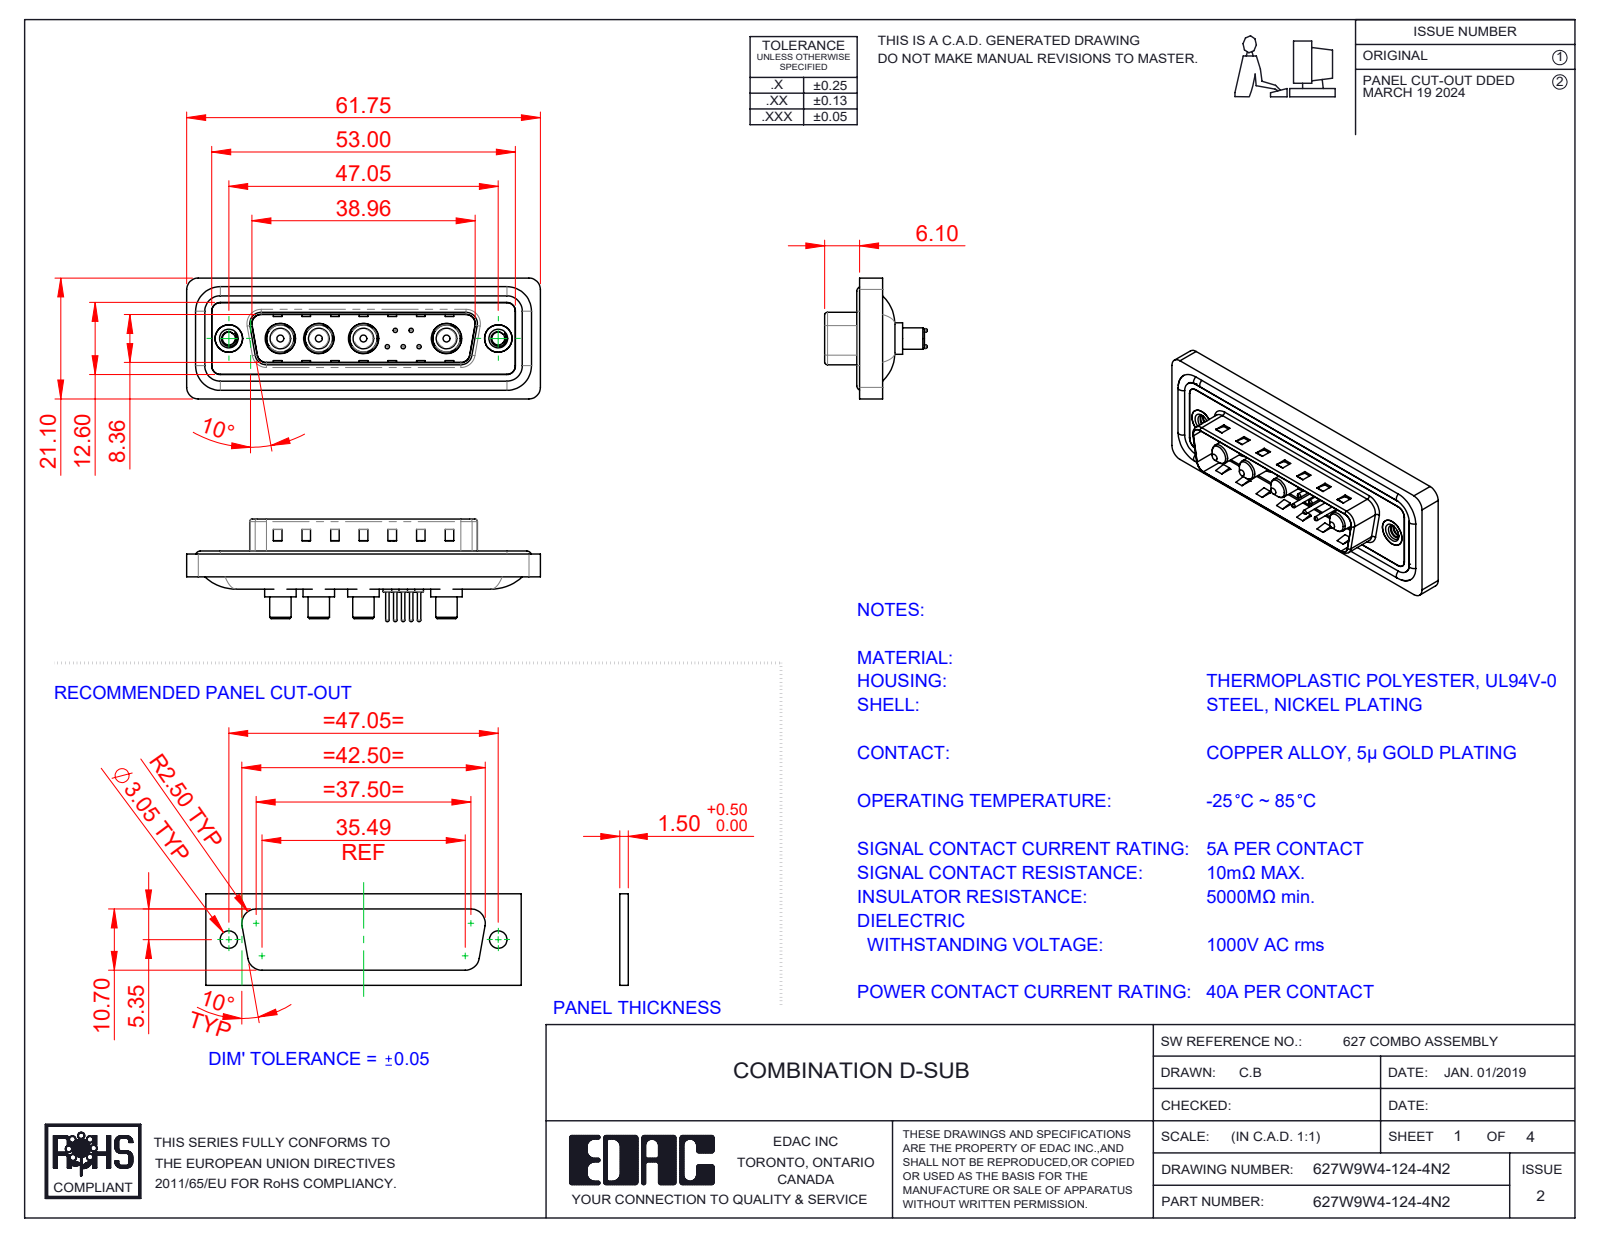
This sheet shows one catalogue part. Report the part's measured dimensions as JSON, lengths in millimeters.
{"part_name": "627Combo Shell Rear_25 Contacts; 627Combo Housing_9W4; 627Combo Threaded Rivet_2; 627Combo Shell Front_25 Contacts (+5 more)", "step_written_by": "SolidWorks 2023 (CONFIG_CONTROL_DESIGN)", "units": "millimeters", "bodies": {"solids": 20, "faces": 824, "planar": 284, "cylindrical": 334, "other": 206}, "overall_size": [61.75, 21.1, 17.9], "volume_mm3": 7478, "surface_area_mm2": 11879, "round_holes": [[0.75, 5], [1.6, 5], [2, 5], [4.85, 4], [5.3, 4], [2.26, 2], [4, 2], [4.8, 2], [5, 2]], "round_bosses_or_shafts": [[1.5, 5], [0.6, 5], [5.5, 4], [5.2, 4], [4.75, 4], [3.75, 4], [3.6, 4], [1.6, 4]], "partial_cylinders_radius": [[1.5, 22], [2, 18], [0.5, 8], [1.6, 8], [0.25, 4], [0.6, 4], [0.65, 4], [0.9, 4]], "face_to_face_distances": [0.4, 1.5, 1.1, 0.5, 1.6, 3.1, 2.9, 0.82, 9.58, 5.65], "hole_center_spacings": [3.16, 2.77, 5.04, 14.51, 2.78, 4.4, 4.41, 5]}
